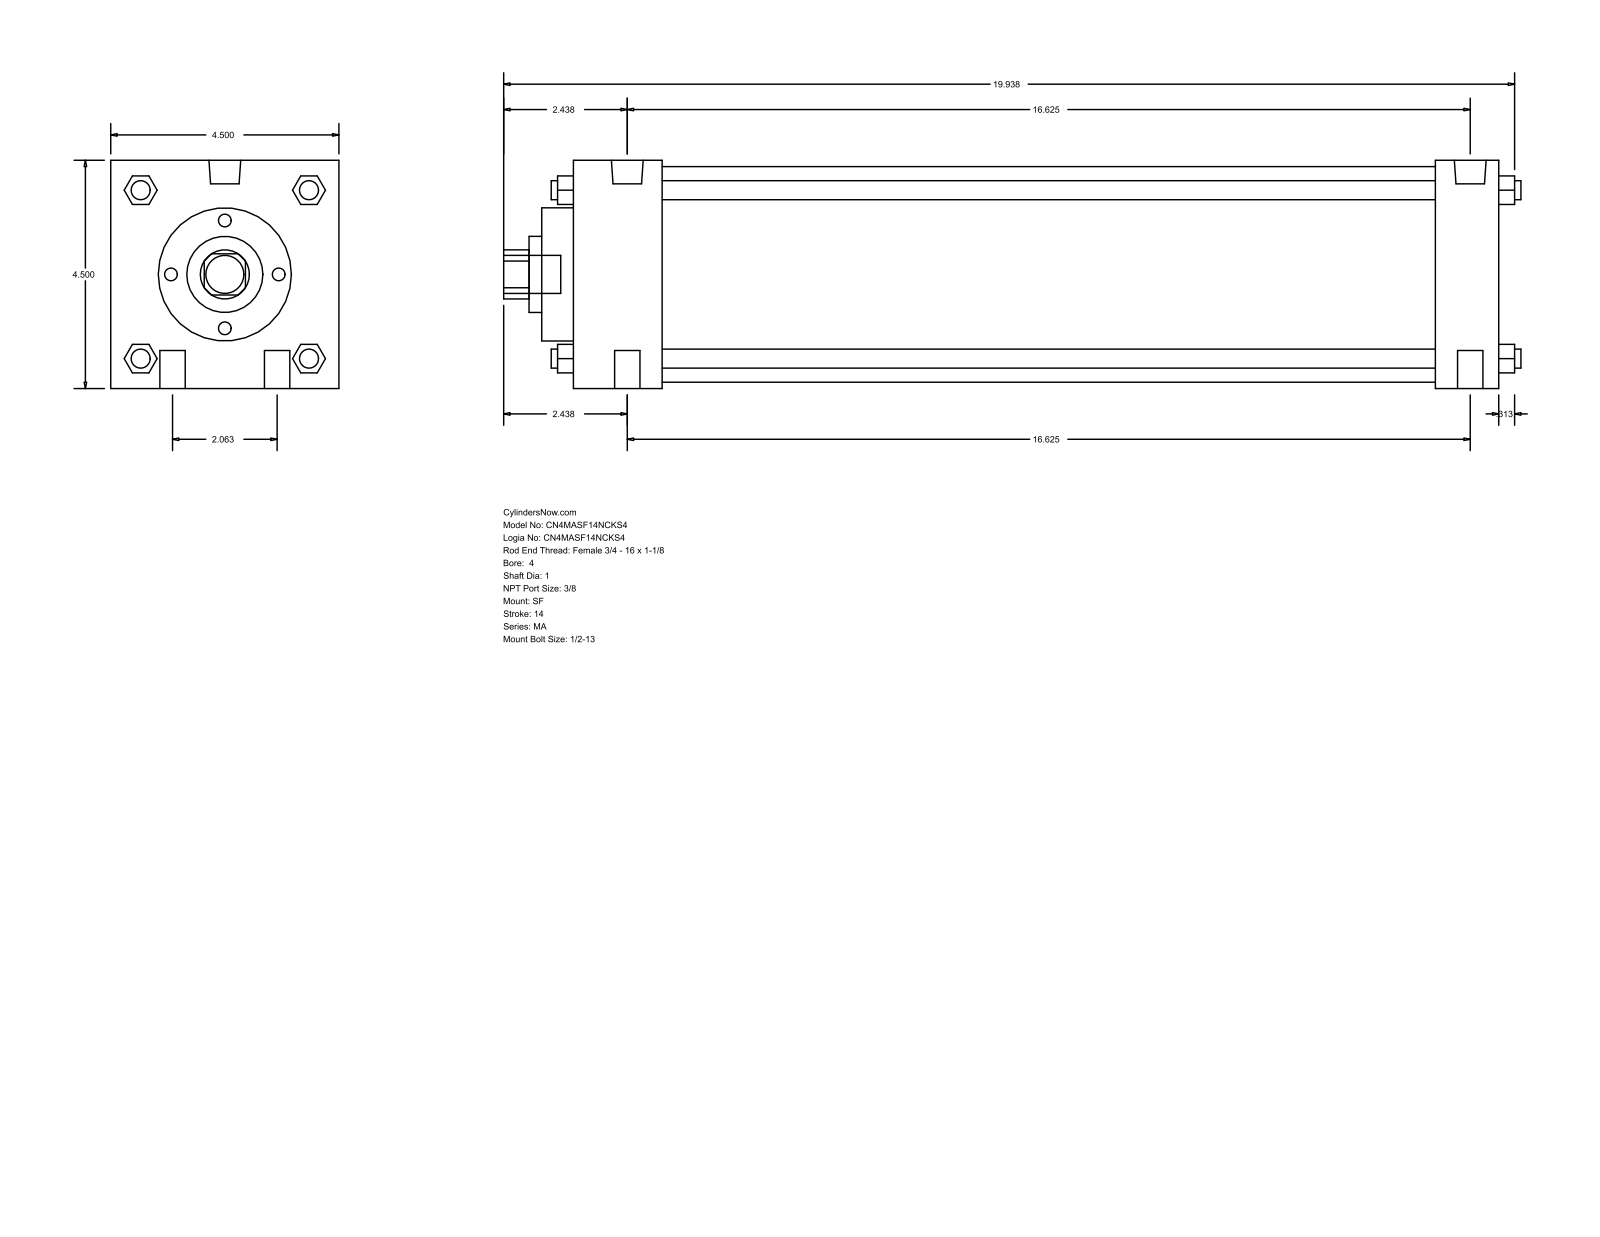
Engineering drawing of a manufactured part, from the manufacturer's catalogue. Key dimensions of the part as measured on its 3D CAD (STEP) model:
Part name (STEP PRODUCT): MA_SF__0400_1
STEP written by: GSSL Pune (CONFIG_CONTROL_DESIGN)
Units: millimetres
Bodies: 0 solids, 126 faces (95 planar, 31 cylindrical, 0 other)
Overall size (bounding box): 509.59 × 114.3 × 114.3
Round holes (diameter × count): ⌀25.4 ×1, ⌀38.1 ×1, ⌀66.67 ×1, ⌀107.95 ×1
Round bosses / shafts (diameter × count): ⌀12.7 ×4, ⌀9.53 ×4, ⌀15.93 ×2, ⌀11.11 ×2, ⌀19.05 ×1
Partial cylindrical surfaces — rounded edges, fillets, slot ends (radius × count): R12.29 ×1
Main face-to-face distances: 114.3, 463.56, 431.81, 31.75, 44.46, 387.35, 419.1, 15.87, 60.33, 447.68
